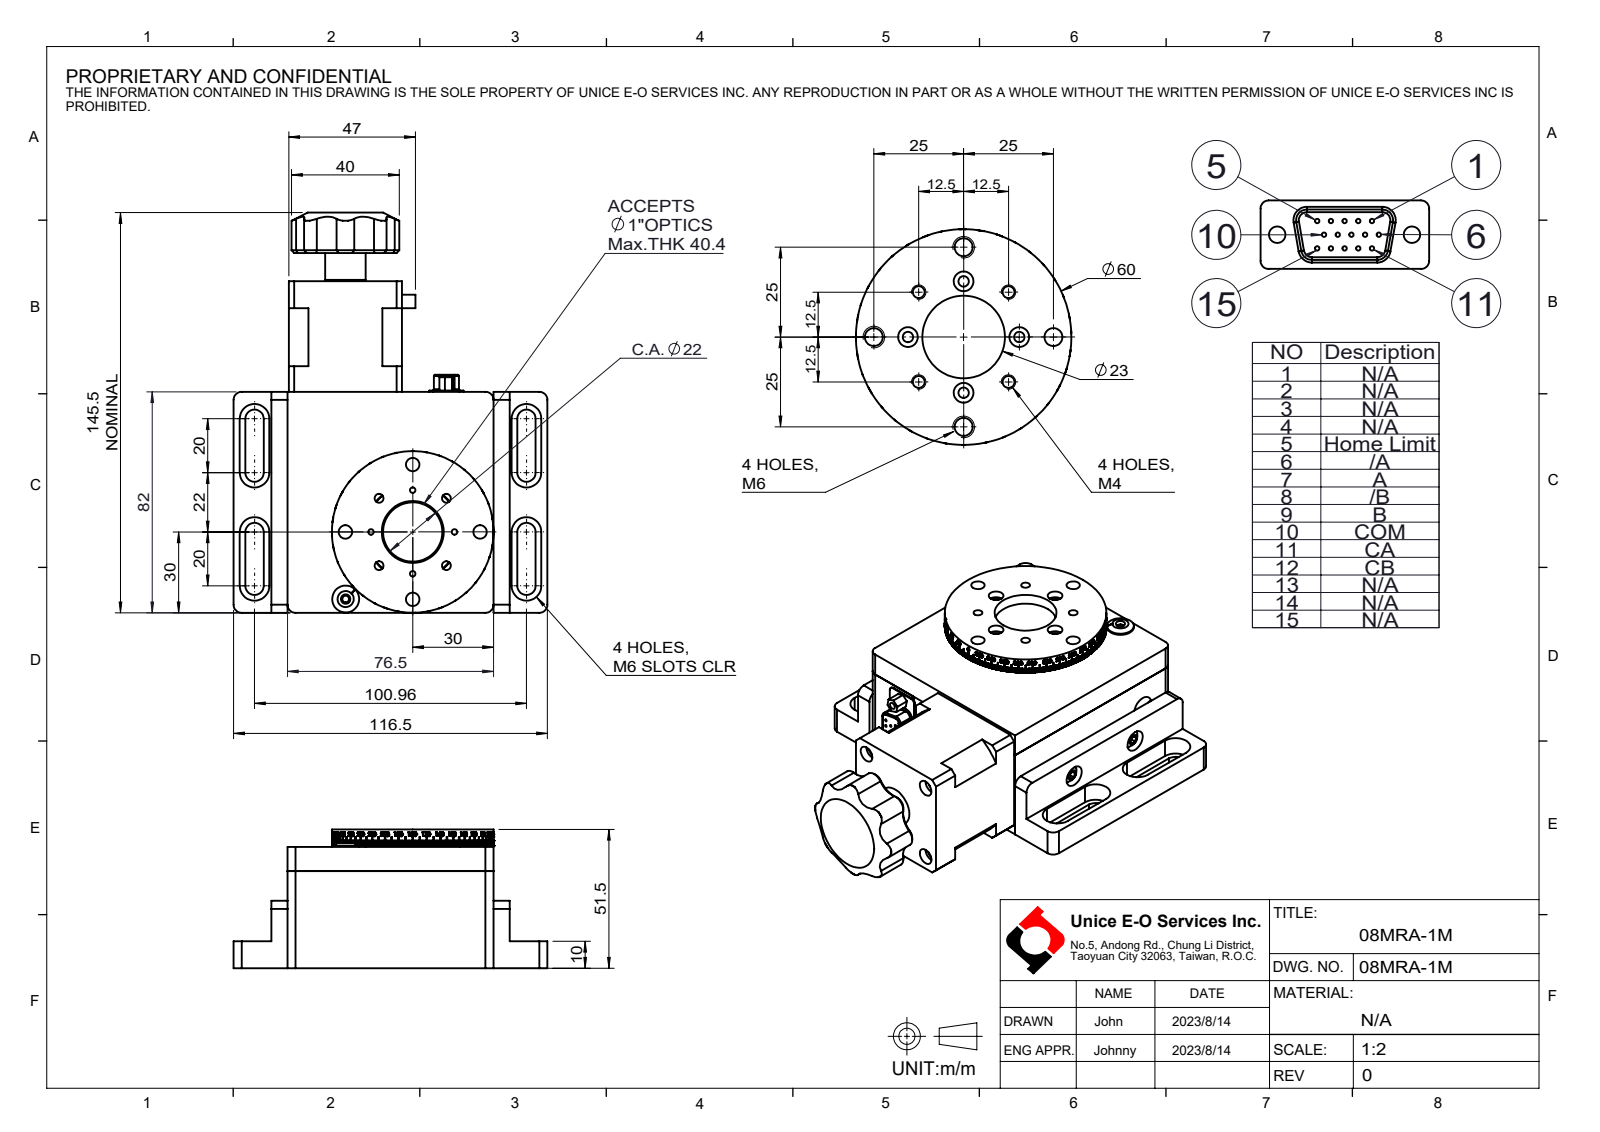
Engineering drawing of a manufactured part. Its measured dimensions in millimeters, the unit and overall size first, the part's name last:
Units: millimetres
Overall size (bounding box): 148.5 × 116.5 × 51.5
Round holes (diameter × count): ⌀0.8 ×15, ⌀3.3 ×6, ⌀2.2 ×4, ⌀2.9 ×4, ⌀5 ×4, ⌀5.5 ×4, ⌀6 ×4, ⌀6.1 ×4, ⌀2.5 ×3, ⌀1.5 ×2, ⌀8 ×2, ⌀1 ×1
Round bosses / shafts (diameter × count): ⌀60 ×1, ⌀43 ×1, ⌀15 ×1, ⌀10 ×1
Partial cylindrical surfaces — rounded edges, fillets, slot ends (radius × count): R3 ×9, R0.5 ×8, R3.4 ×8, R4 ×8, R5.5 ×8, R7.41 ×8, R1.5 ×4, R2 ×4
Main face-to-face distances: 36, 45, 76.5, 9, 0.5, 82, 6, 6.5, 42, 34
Hole centre spacings: 2.84, 4.58, 5.08, 2.54, 17.68, 6.84, 25, 5.68
Bodies: 0 solids, 929 faces (377 planar, 352 cylindrical, 200 other)
Part name (STEP PRODUCT): 08MRA-1M
STEP written by: SolidWorks 2016 (AUTOMOTIVE_DESIGN)
